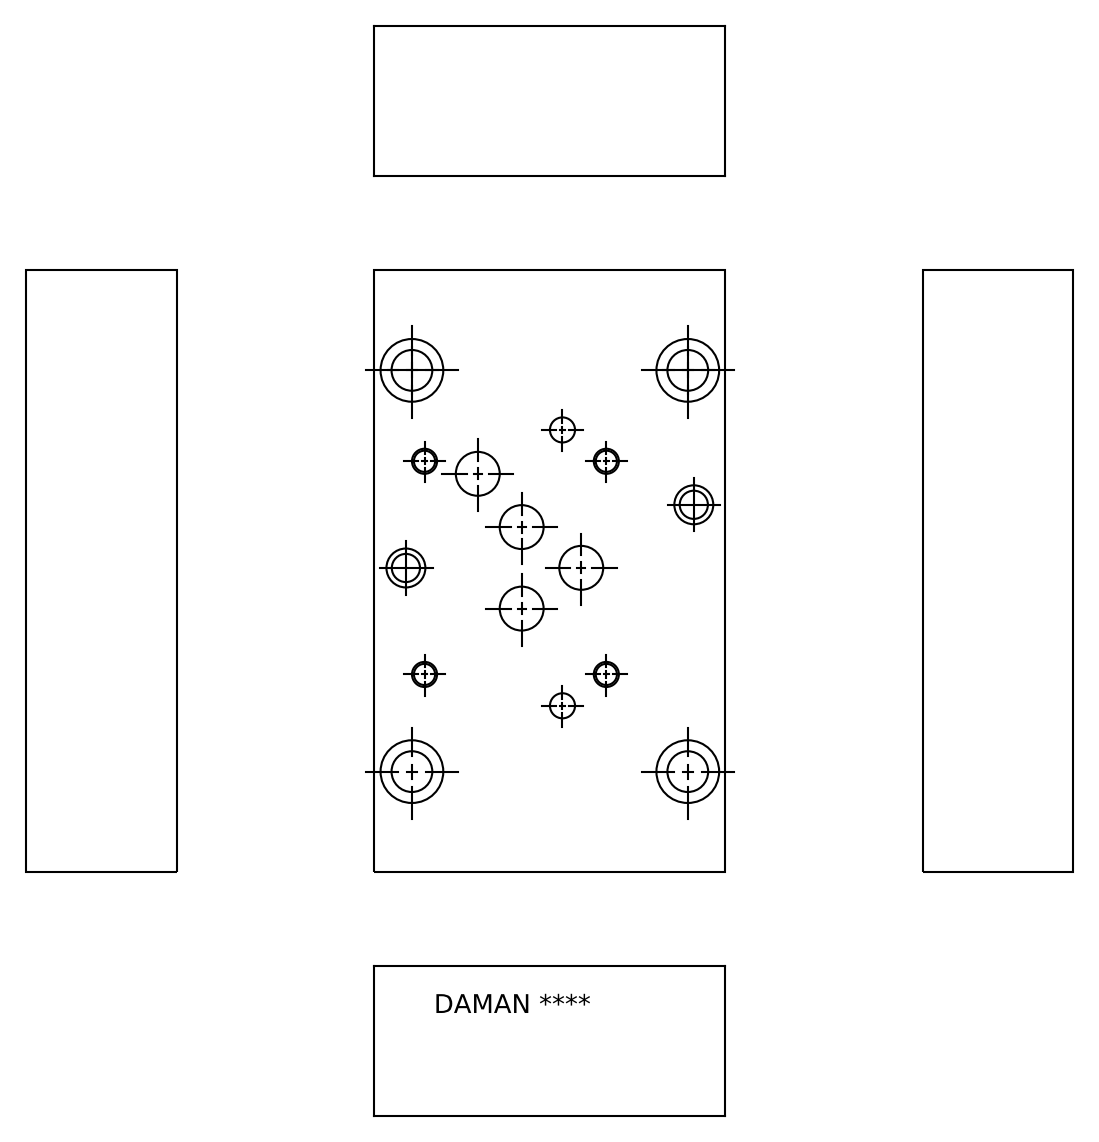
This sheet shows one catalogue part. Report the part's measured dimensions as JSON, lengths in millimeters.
{"part_name": "Part_AD05HED07VAAB.C01734R4_3D", "step_written_by": "Autodesk Inventor 2022 (AUTOMOTIVE_DESIGN)", "units": "millimeters", "bodies": {"solids": 1, "faces": 424, "planar": 285, "cylindrical": 44, "other": 95}, "overall_size": [152.4, 88.9, 38.1], "volume_mm3": 481939, "surface_area_mm2": 55817, "round_holes": [[11.13, 10], [6.35, 7], [5.11, 6], [10.31, 6], [15.88, 5], [25.4, 4], [3.17, 2], [7.14, 2], [11.11, 2]], "face_to_face_distances": [38.1, 88.9, 152.4, 2.79, 35.31, 23.88, 21.09, 14.22, 1.32, 1.47], "hole_center_spacings": [14.61, 44.22, 69.85, 15.55, 22.45, 22.46, 26.69, 27.71]}
